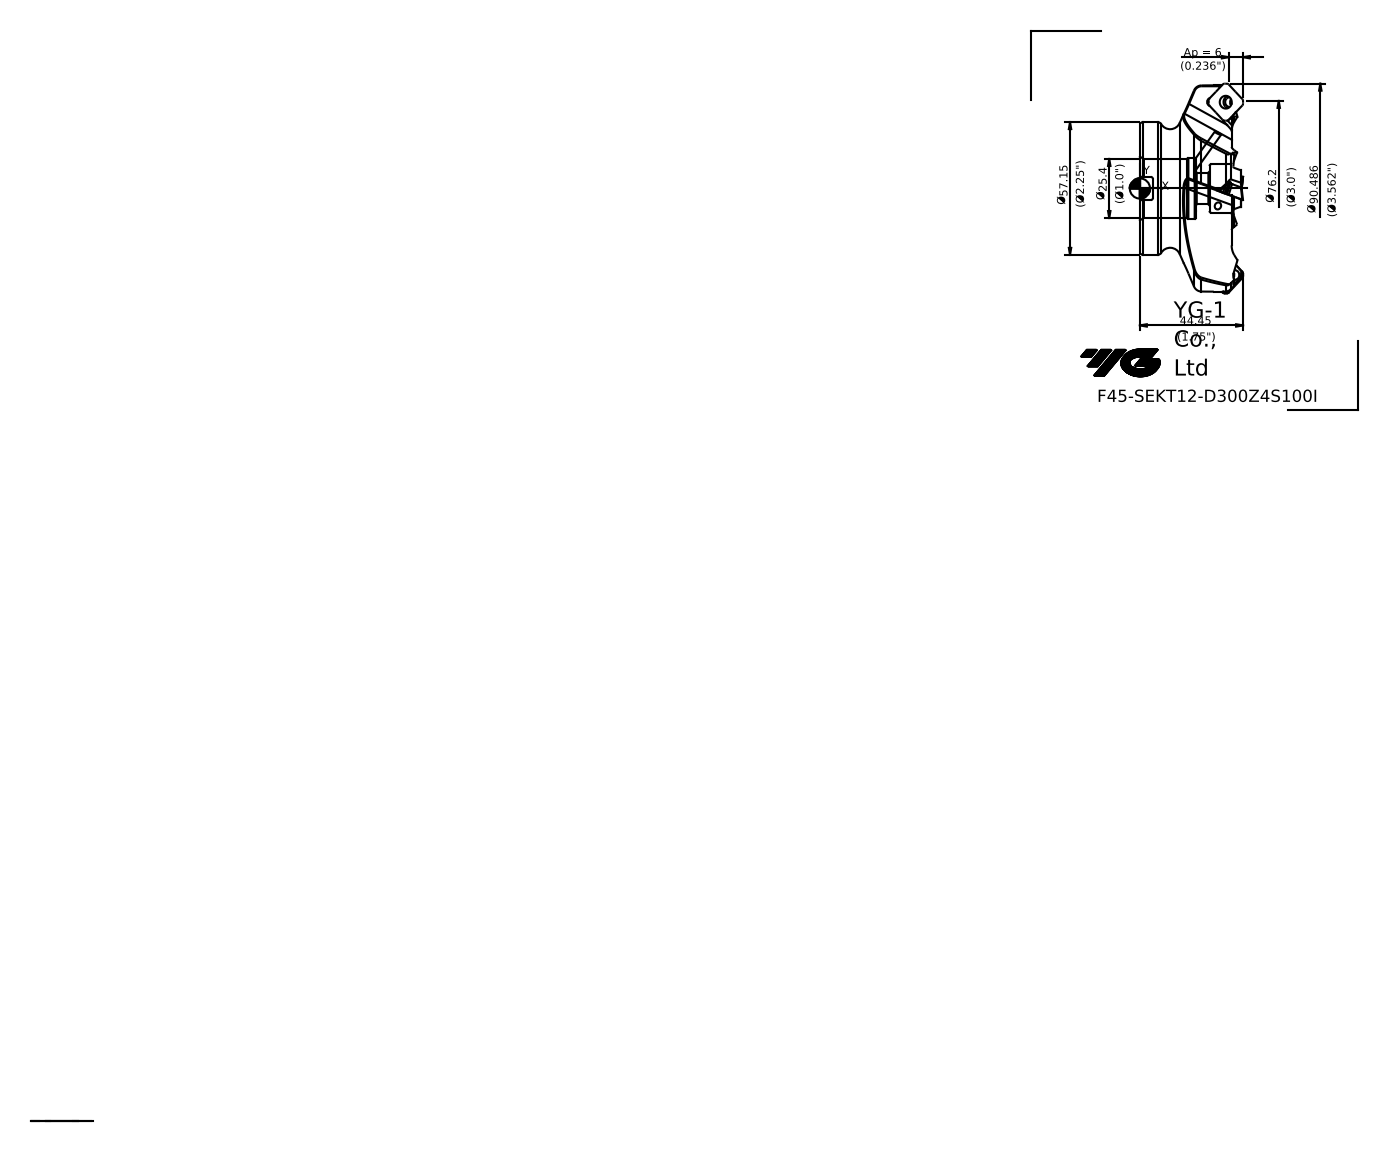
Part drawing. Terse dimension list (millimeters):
name: 102227FC3665cok5
written by: SIEMENS PLM Software NX 10.0 (AP203_CONFIGURATION_CONTROLLED_3D_DESIGN_OF_MECHANICAL_PARTS_AND_ASSEMBLIES_MIM_LF)
unit: mm
bodies: 1 solid, 67 faces (16 planar, 10 cylindrical, 41 other)
size: 90.49 × 90.49 × 44.45
volume: 153 566 mm³; area: 33 971 mm²
holes: 1× ⌀13.69, 1× ⌀21.01, 1× ⌀25.4, 1× ⌀26.4
bosses: 1× ⌀88.91, 1× ⌀57.15
rounds: 2× R0.8
face distances: 39.54, 15.54, 24, 33.98, 18.44, 5.56, 9.94, 9.54, 6, 24.44
